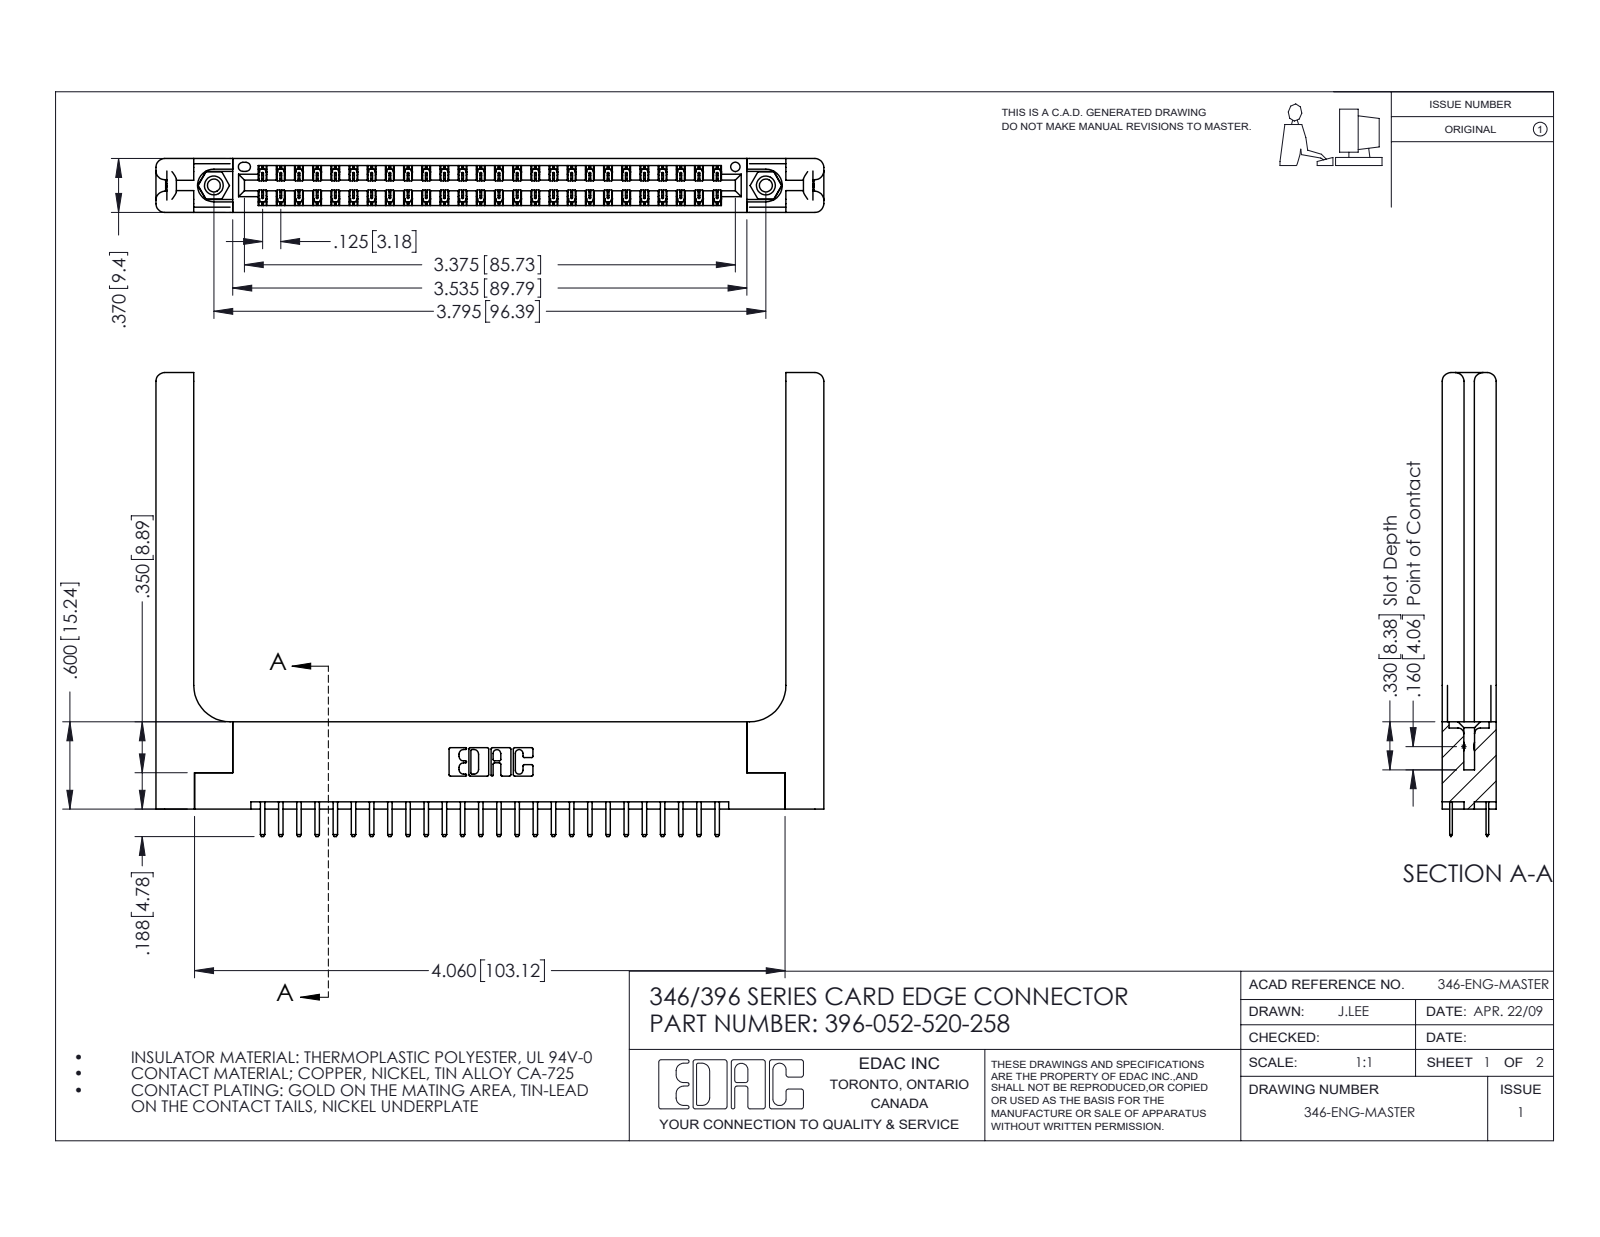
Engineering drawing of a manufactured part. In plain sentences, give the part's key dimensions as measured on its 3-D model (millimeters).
The part is named "345-292-001_345-293-120; 396-052-520-258; 345-250-001_345-250-001-102; 346-220-058_345-220-058 (+1 more)". Its 3-D file was written by "SolidWorks 2016 (CONFIG_CONTROL_DESIGN)". It is 57 solids with 3290 faces: 2148 planar, 1082 cylindrical and 60 other. Overall it measures 116.6 by 81 by 9.4 millimeters. Its volume is 18 710 cubic millimeters and its surface area 20 100 square millimeters. Round holes: 2 of diameter 2.3, 2 of diameter 3.2, 2 of diameter 4, 1 of diameter 1.6. Round bosses or shafts: 2 of diameter 3.9. Partial cylindrical surfaces (rounded edges, fillets, slot ends): 78 of radius 0.2, 56 of radius 0.3, 22 of radius 0.3, 16 of radius 1.5, 6 of radius 0.2, 6 of radius 0.8, 3 of radius 0.7, 2 of radius 0.4. The main face-to-face distances are 9.4, 1.8, 1.2, 8.2, 3.8, 3.8, 6.4, 7.6, 0.6, 7. The hole center spacings are 6.2, 91.1, 96.4.
